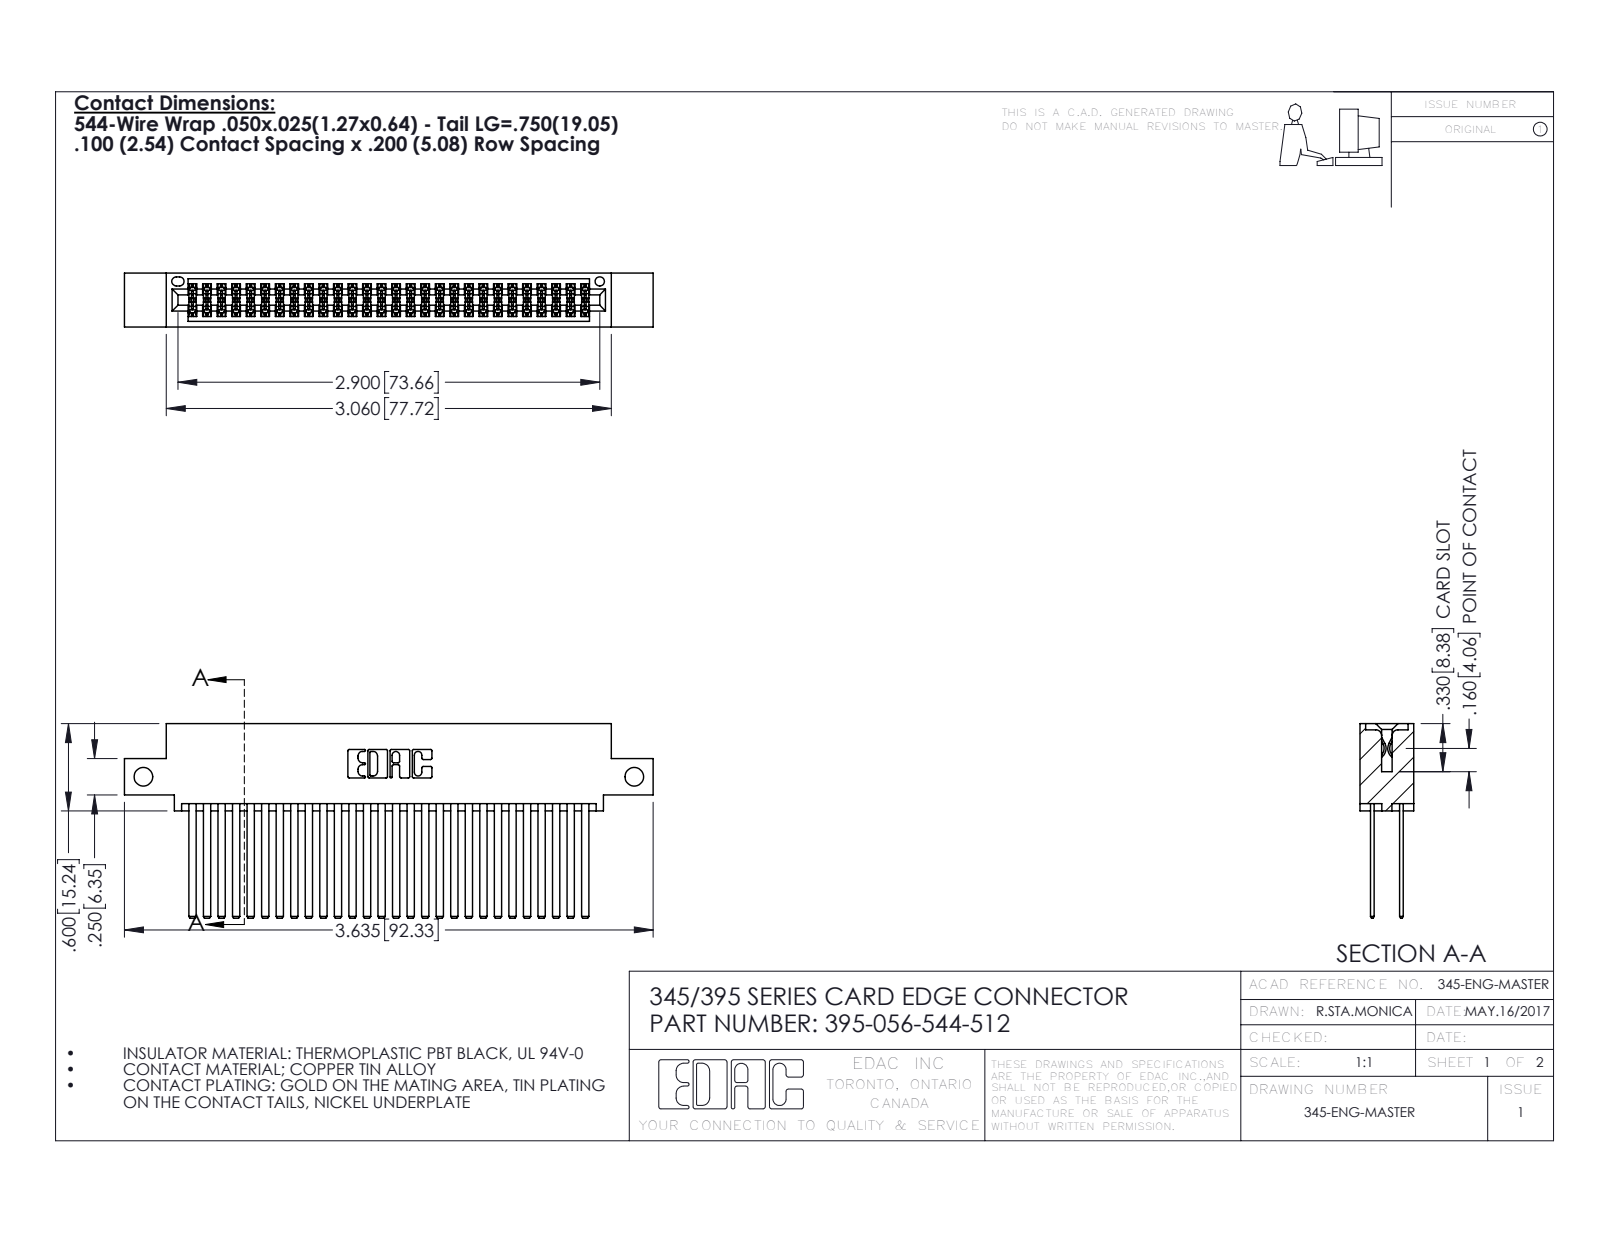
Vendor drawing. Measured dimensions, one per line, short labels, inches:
name: 395-056-544-512; 345 Part_0.110 Offset - Side Mount; 345-292-001_345-293-144
written by: SolidWorks 2016 (CONFIG_CONTROL_DESIGN)
unit: in
bodies: 57 solids, 2594 faces (1708 planar, 886 cylindrical, 0 other)
size: 3.635 × 1.337 × 0.37
volume: 0.577 in³; area: 24.76 in²
holes: 2× ⌀0.128, 1× ⌀0.064
rounds: 84× R0.006, 22× R0.01, 6× R0.007, 6× R0.031, 3× R0.026, 2× R0.014, 2× R0.019, 2× R0.022
face distances: 0.2, 0.025, 0.298, 0.072, 0.098, 0.272, 0.225, 0.175, 0.37, 0.05
hole spacings: 3.375
